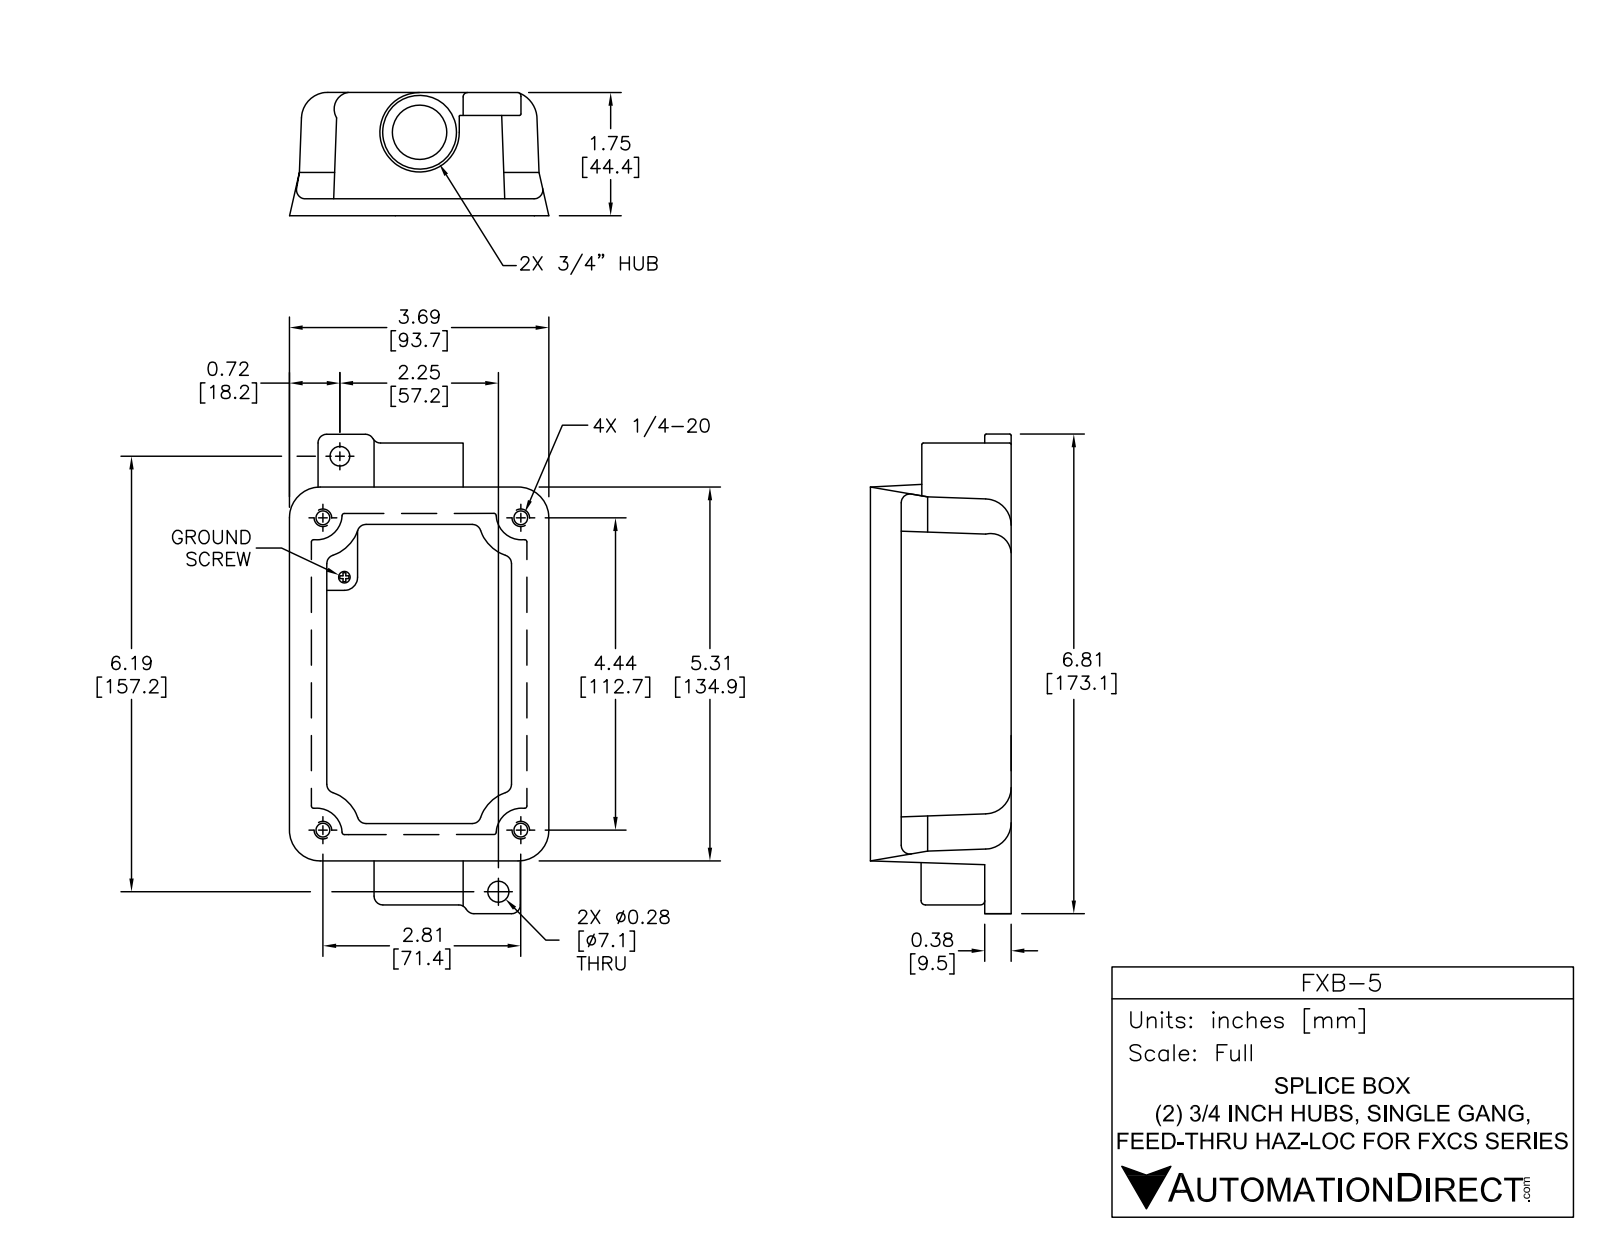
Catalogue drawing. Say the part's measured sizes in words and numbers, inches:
The part is named "FXB-5". Its 3-D file was written by "SolidWorks 2015 (AUTOMOTIVE_DESIGN)". It is 2 solids with 372 faces: 114 planar, 102 cylindrical and 156 other. Overall it measures 7.026 by 3.746 by 1.8 inches. Its volume is 14.45 cubic inches and its surface area 101.2 square inches. Round holes: 4 of diameter 0.266, 2 of diameter 0.32, 2 of diameter 0.772, 2 of diameter 0.95. Round bosses or shafts: 1 of diameter 0.325. Partial cylindrical surfaces (rounded edges, fillets, slot ends): 26 of radius 0.02, 16 of radius 0.01, 12 of radius 0.1, 8 of radius 0.22, 4 of radius 0.26, 4 of radius 0.633, 2 of radius 0.36, 2 of radius 0.468. The main face-to-face distances are 0.275, 0.29, 2.9, 1.525, 1.8, 2.61, 3.19, 4.818, 0.548, 4.27. The hole center spacings are 0.437, 0.925, 1.013, 2.749, 2.769, 2.812, 2.867, 4.44.
